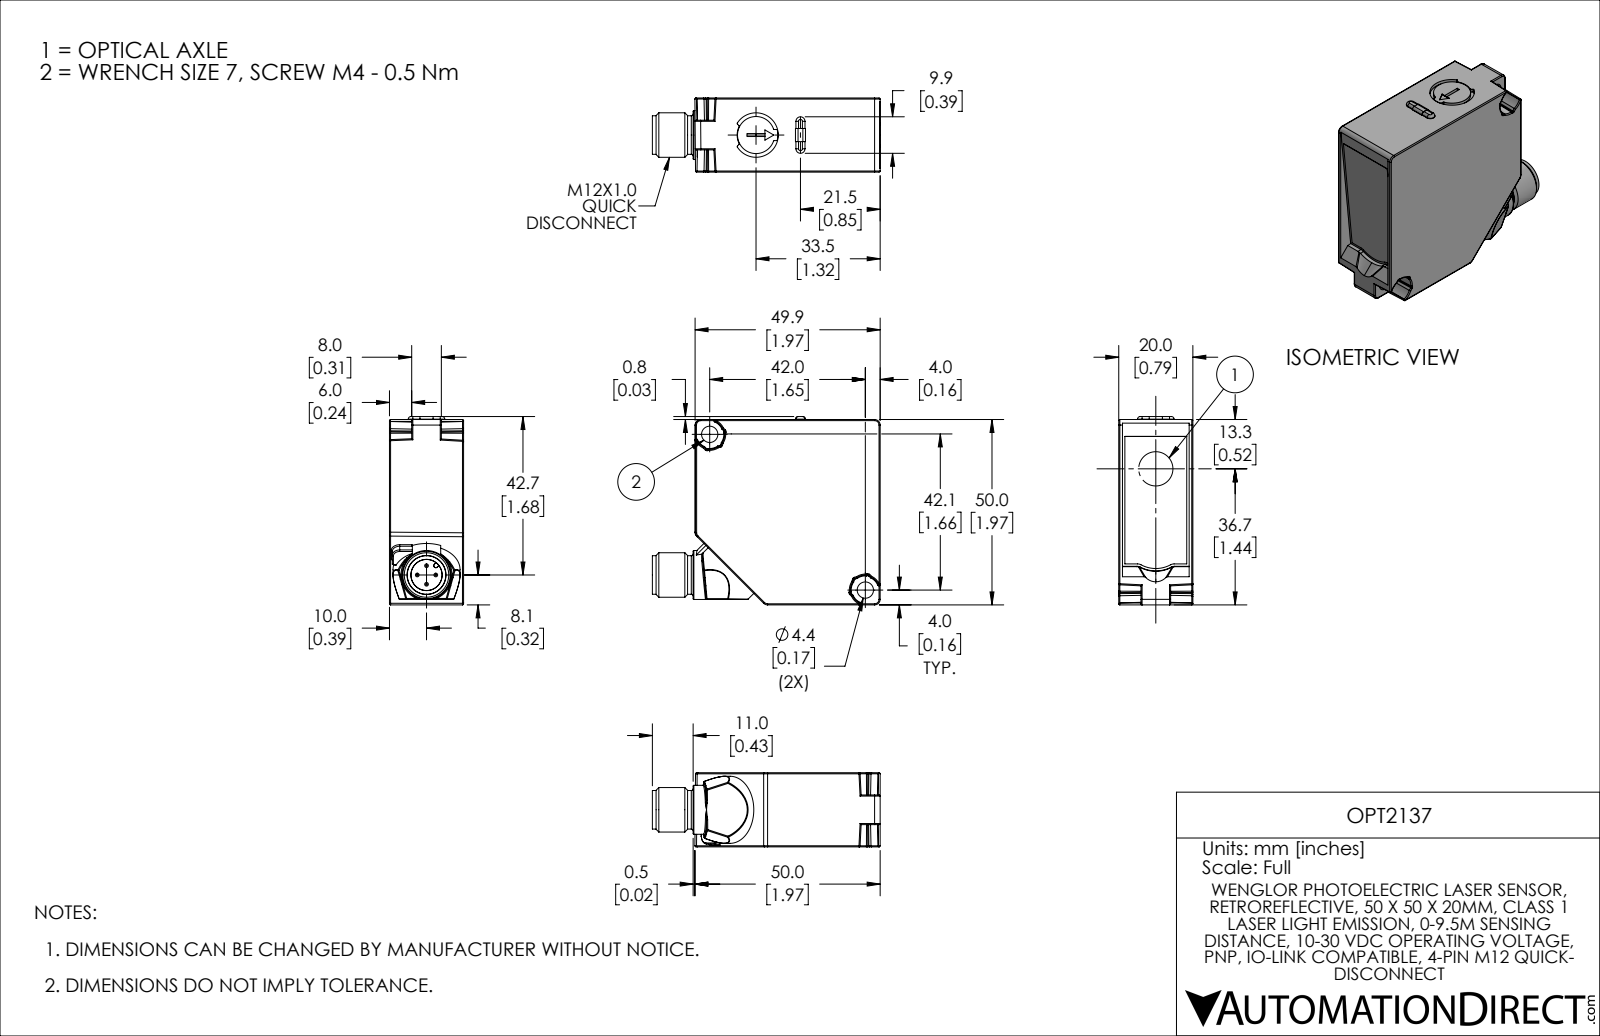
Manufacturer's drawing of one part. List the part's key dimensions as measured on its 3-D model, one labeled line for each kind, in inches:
Part name (STEP PRODUCT): OPT2137
STEP written by: SolidWorks 2019 (AUTOMOTIVE_DESIGN)
Units: inches
Bodies: 2 solids, 347 faces (111 planar, 121 cylindrical, 115 other)
Overall size (bounding box): 2.853 × 2 × 0.787
Volume: 2.816 in³ · Surface area: 15.65 in²
Round holes (diameter × count): ⌀0.173 ×2, ⌀0.472 ×1, ⌀0.713 ×1
Round bosses / shafts (diameter × count): ⌀0.039 ×4, ⌀0.52 ×1, ⌀0.472 ×1, ⌀0.409 ×1, ⌀0.394 ×1, ⌀0.008 ×1
Partial cylindrical surfaces — rounded edges, fillets, slot ends (radius × count): R0.012 ×64, R0.008 ×8, R0.059 ×5, R0.079 ×5, R0.028 ×4, R0.048 ×2, R0.201 ×1, R0.232 ×1
Main face-to-face distances: 0.787, 1.969, 0.039, 0.748, 0.236, 0.551, 0.197, 0.512, 0.058, 1.911
Hole centre spacings: 2.339
